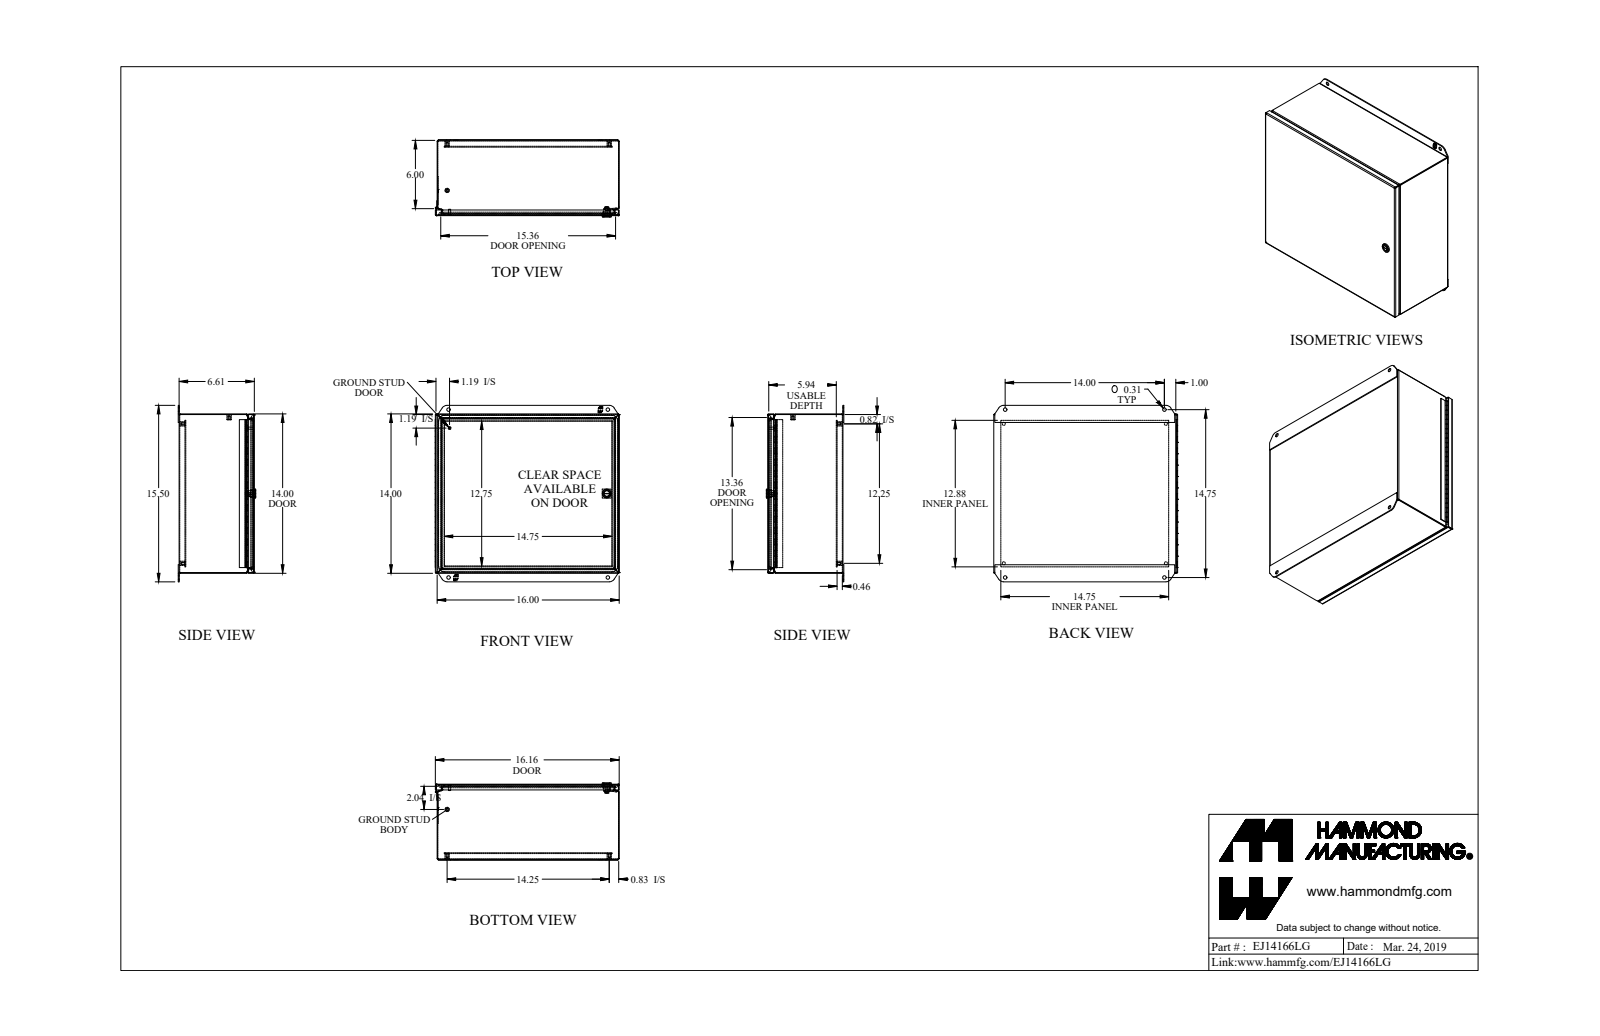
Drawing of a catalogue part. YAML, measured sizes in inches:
part_name: "EJ14166LG_Default"
step_written_by: "SolidWorks 2019 (CONFIG_CONTROL_DESIGN)"
units: inches
bodies: {solids: 16, faces: 739, planar: 409, cylindrical: 238, other: 92}
overall_size: [16.165, 15.5, 6.805]
volume: 73.16
surface_area: 2407
round_holes:
  - {diameter: 0.156, count: 5}
  - {diameter: 0.265, count: 4}
  - {diameter: 0.313, count: 4}
  - {diameter: 0.05, count: 1}
  - {diameter: 0.516, count: 1}
round_bosses_or_shafts:
  - {diameter: 0.375, count: 5}
  - {diameter: 0.788, count: 1}
  - {diameter: 0.535, count: 1}
  - {diameter: 0.496, count: 1}
  - {diameter: 0.435, count: 1}
  - {diameter: 0.25, count: 1}
  - {diameter: 0.188, count: 1}
  - {diameter: 0.1, count: 1}
partial_cylinders:
  - {radius: 0.029, count: 16}
  - {radius: 0.086, count: 16}
  - {radius: 0.281, count: 10}
  - {radius: 0.25, count: 4}
  - {radius: 0.499, count: 4}
  - {radius: 0.5, count: 4}
  - {radius: 0.06, count: 2}
  - {radius: 0.539, count: 2}
face_to_face_distances: [0.057, 6.554, 0.072, 0.589, 6.611, 6.497, 13.943, 0.46, 0.517, 6.094]
hole_center_spacings: [19.539, 1.256, 13.5, 14.18, 12.25, 12.25, 14.25, 14.25]
